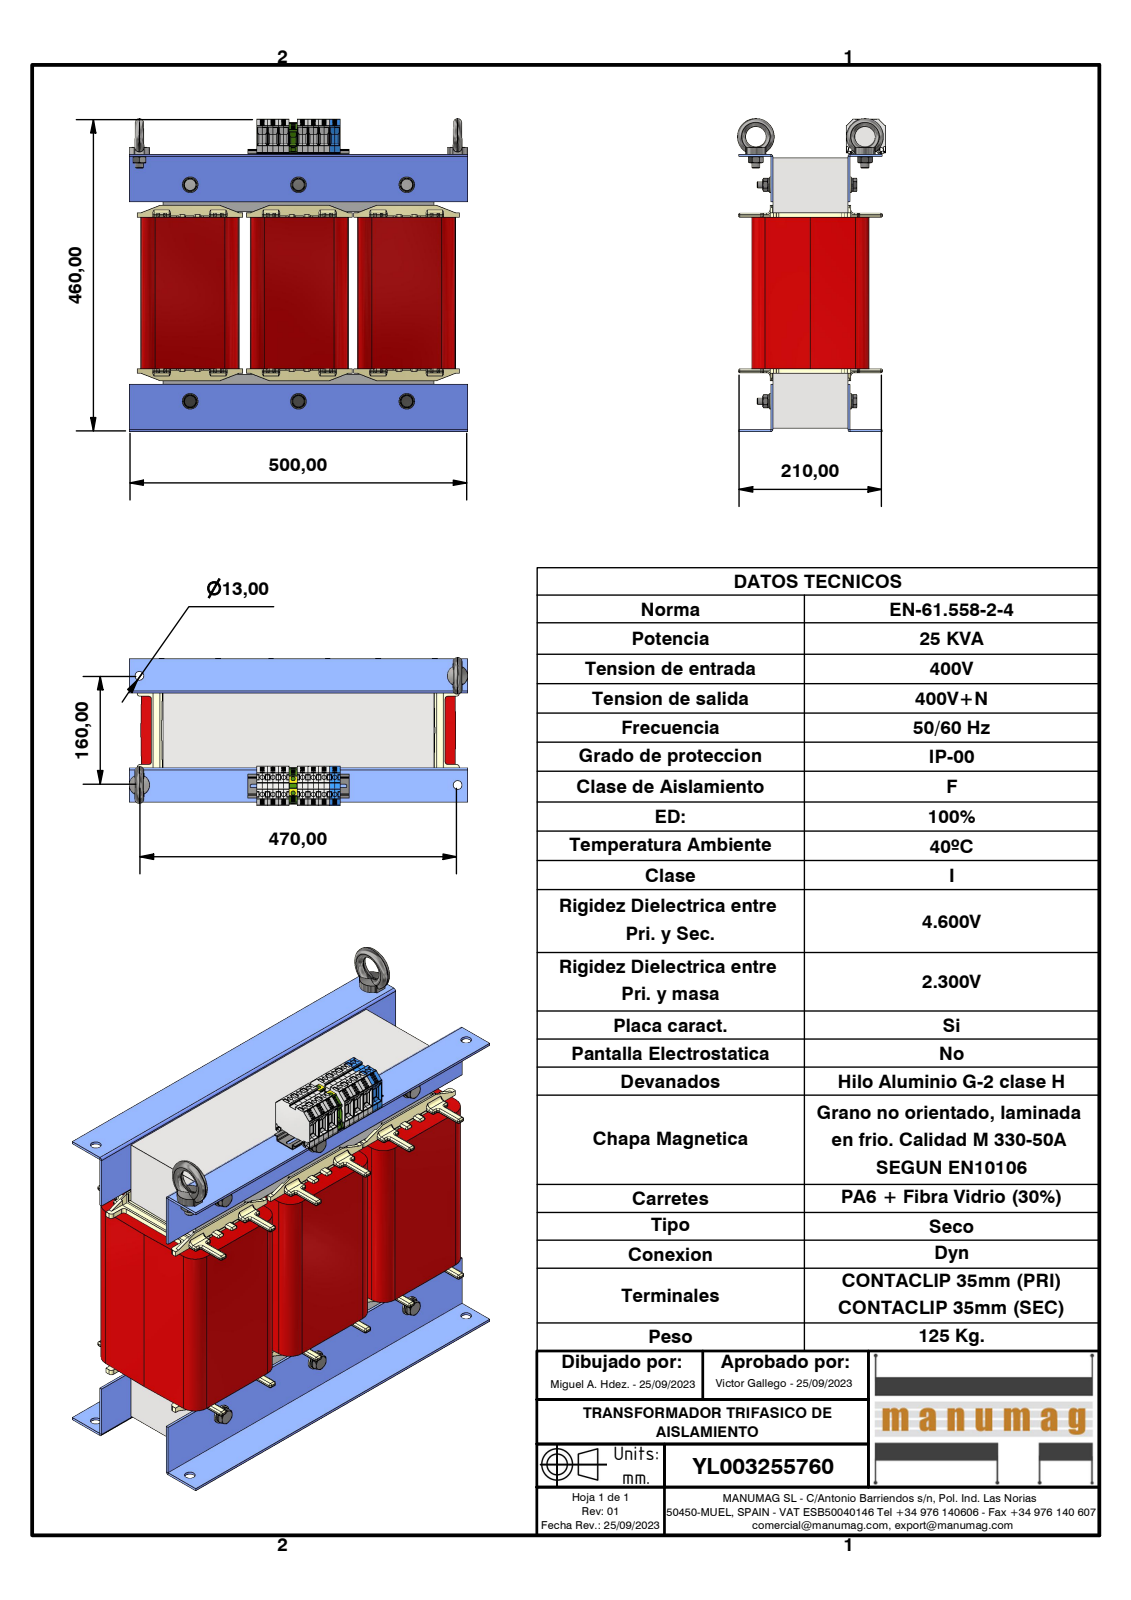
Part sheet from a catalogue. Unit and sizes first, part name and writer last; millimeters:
Units: millimetres
Overall size (bounding box): 500 × 463 × 217.3
Round holes (diameter × count): ⌀6.5 ×14, ⌀13 ×10, ⌀8.38 ×6, ⌀10 ×6, ⌀10.5 ×6, ⌀15 ×6, ⌀2 ×4, ⌀6.3 ×2, ⌀10.11 ×2, ⌀30 ×2
Round bosses / shafts (diameter × count): ⌀0.6 ×12, ⌀23 ×6, ⌀20 ×6, ⌀15.4 ×6, ⌀11.5 ×6, ⌀9.19 ×6, ⌀54 ×2, ⌀12 ×2
Partial cylindrical surfaces — rounded edges, fillets, slot ends (radius × count): R0.3 ×494, R2 ×202, R0.5 ×188, R1 ×90, R0.25 ×34, R0.81 ×33, R1.9 ×32, R4 ×26
Main face-to-face distances: 3, 320, 110, 6, 30.86, 113, 116, 2, 116.2, 24.85
Hole centre spacings: 15.9, 29.63, 25, 160, 31.8, 40.45, 59.6, 64.63
Volume: 24 370 000 mm³ · Surface area: 2 676 000 mm²
Bodies: 57 solids, 8917 faces (4885 planar, 2650 cylindrical, 1382 other)
Part name (STEP PRODUCT): YL003255760; 3UI240 400 x 400 - 110; UI 240_110_BOBINADO; RC80 NT080 (+8 more)
STEP written by: Autodesk Inventor 2023 (AUTOMOTIVE_DESIGN)
